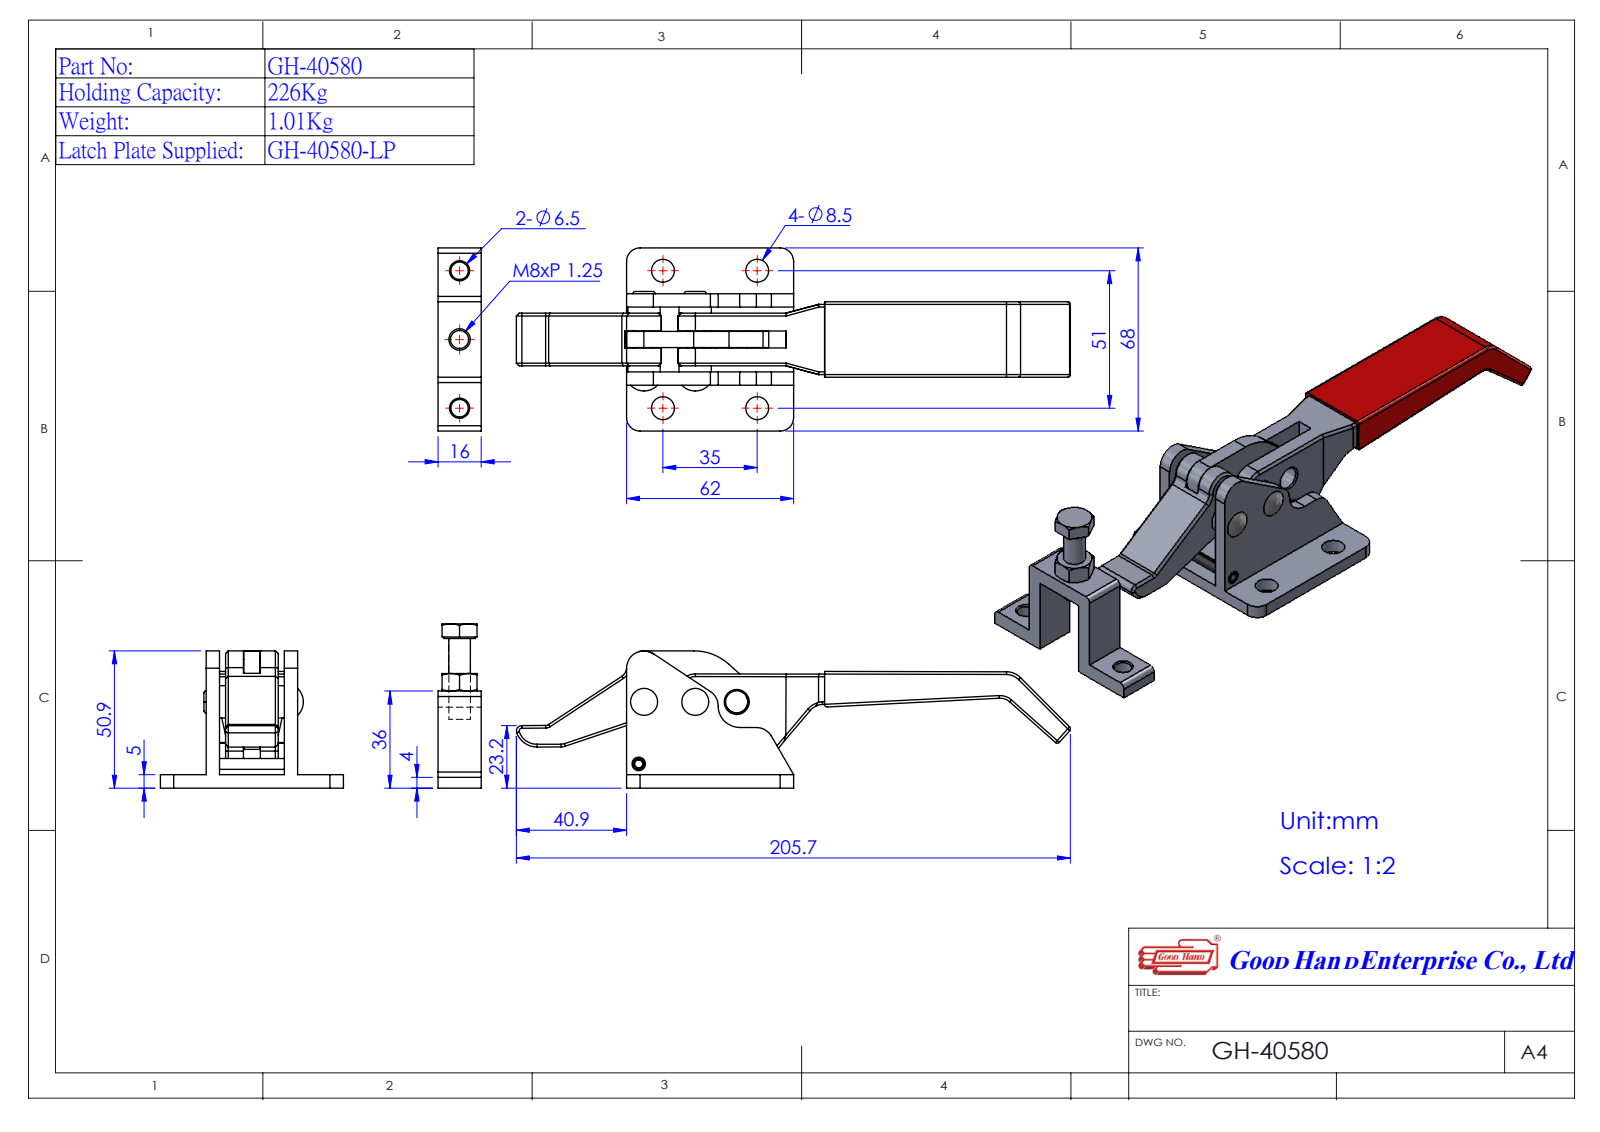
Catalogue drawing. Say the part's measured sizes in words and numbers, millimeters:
The part is named "14058005-連桿-1^GH-40580(簡化); Group5^GH-40580(簡化); Group4^GH-40580(簡化); Group2^GH-40580(簡化) (+3 more)". Its 3-D file was written by "SolidWorks 2016 (AUTOMOTIVE_DESIGN)". It is 6 solids with 266 faces: 116 planar, 118 cylindrical and 32 other. Overall it measures 308.23 by 68 by 61.93 millimeters. Its volume is 135 881 cubic millimeters and its surface area 53 094 square millimeters. Round holes: 4 of diameter 5, 4 of diameter 8.5, 2 of diameter 6.5, 2 of diameter 8.3, 1 of diameter 2.6, 1 of diameter 6.75, 1 of diameter 6.8. Round bosses or shafts: 3 of diameter 6.3, 2 of diameter 16, 2 of diameter 9, 2 of diameter 4, 1 of diameter 11.63, 1 of diameter 8. Partial cylindrical surfaces (rounded edges, fillets, slot ends): 9 of radius 6.4, 6 of radius 5, 2 of radius 2, 2 of radius 3, 2 of radius 4, 2 of radius 8, 1 of radius 4.4, 1 of radius 4.4. The main face-to-face distances are 5, 7.25, 2, 20, 27, 26.75, 12.9, 13.85, 20.15, 6.6. The hole center spacings are 51, 25.5, 35, 61.85, 147.98, 150.16, 156.52, 182.98.
